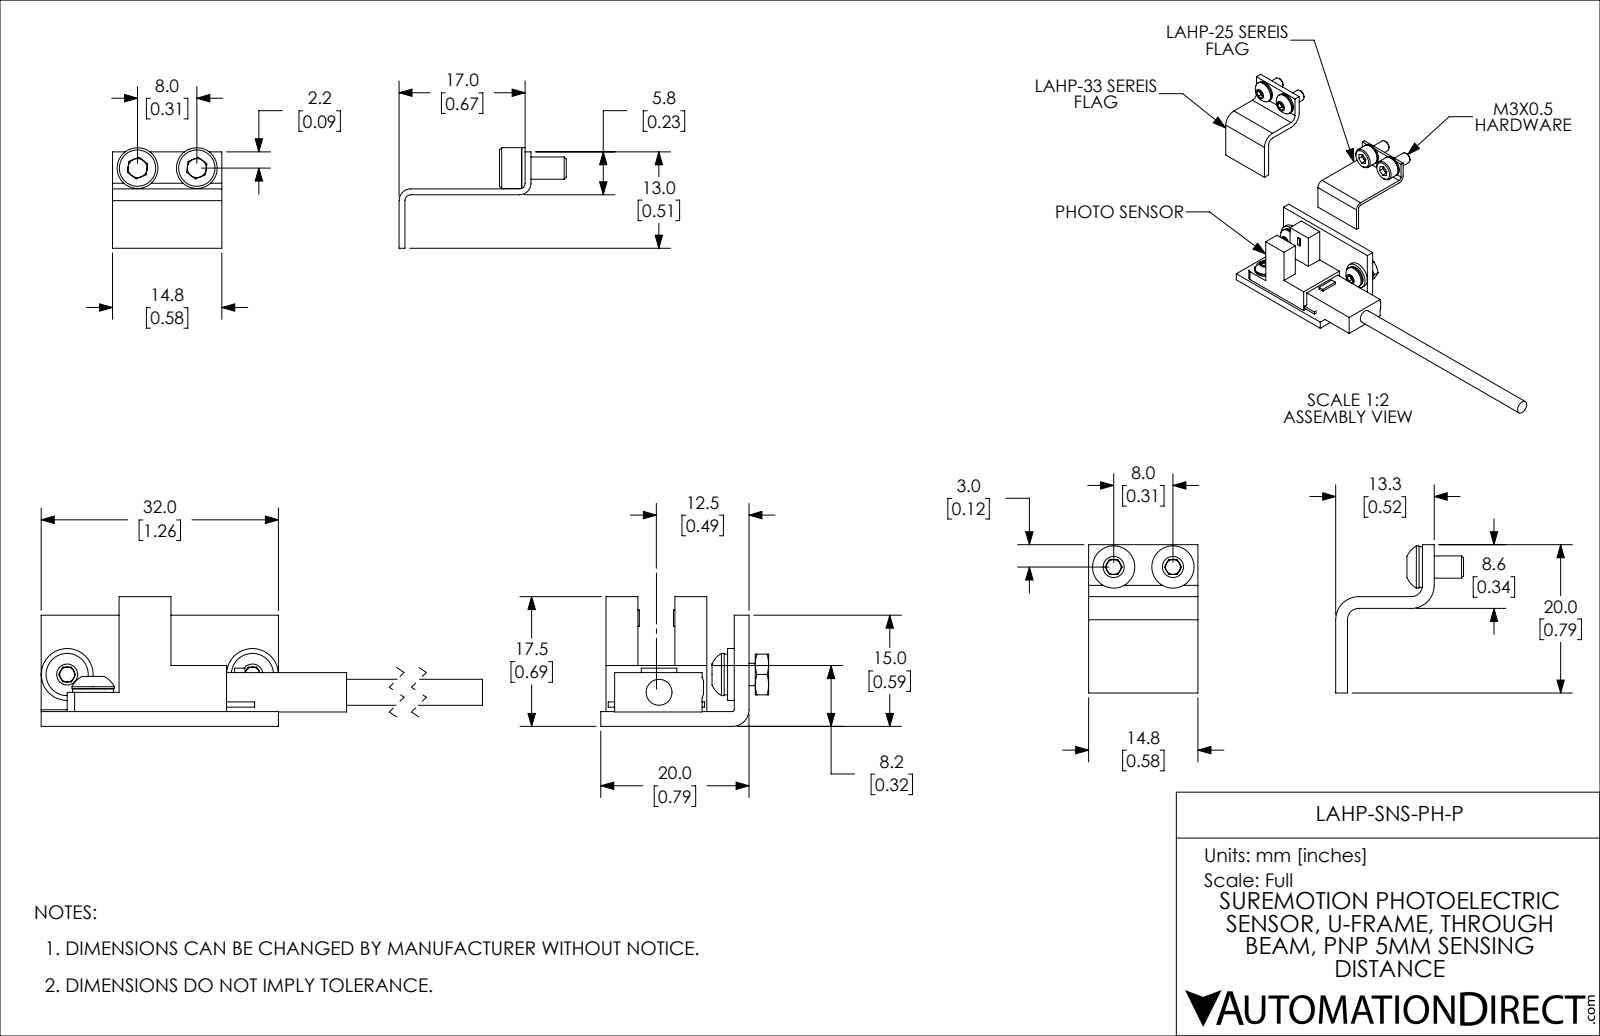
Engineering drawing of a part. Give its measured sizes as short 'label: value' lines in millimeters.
name: LAHP-SNS-PH-P_25-FLAG; LAHP-SNS-PH-P; LAHP-SNS-PH-P_33-FLAG; LAHP-SNS-PH-P_PHOTO SENSOR
written by: SolidWorks 2019 (CONFIG_CONTROL_DESIGN)
unit: mm
bodies: 26 solids, 572 faces (276 planar, 160 cylindrical, 136 other)
size: 111.9 × 52.5 × 29.6
volume: 7 290 mm³; area: 9 303 mm²
holes: 10× ⌀3.2, 6× ⌀2.6, 4× ⌀1, 4× ⌀2.5, 4× ⌀3.4, 2× ⌀3, 2× ⌀3.5, 2× ⌀3.7
bosses: 8× ⌀5.5, 6× ⌀5.7, 6× ⌀3, 2× ⌀7, 1× ⌀3.5
rounds: 8× R0.5, 2× R1, 2× R1.3, 2× R1.5, 1× R0.3, 1× R0.8, 1× R0.8, 1× R1.5
face distances: 2, 0.5, 2.6, 7, 6, 7.6, 5, 2.9, 10, 2.6
hole spacings: 8, 35.3, 2.5, 5.1, 7, 8, 8, 18
